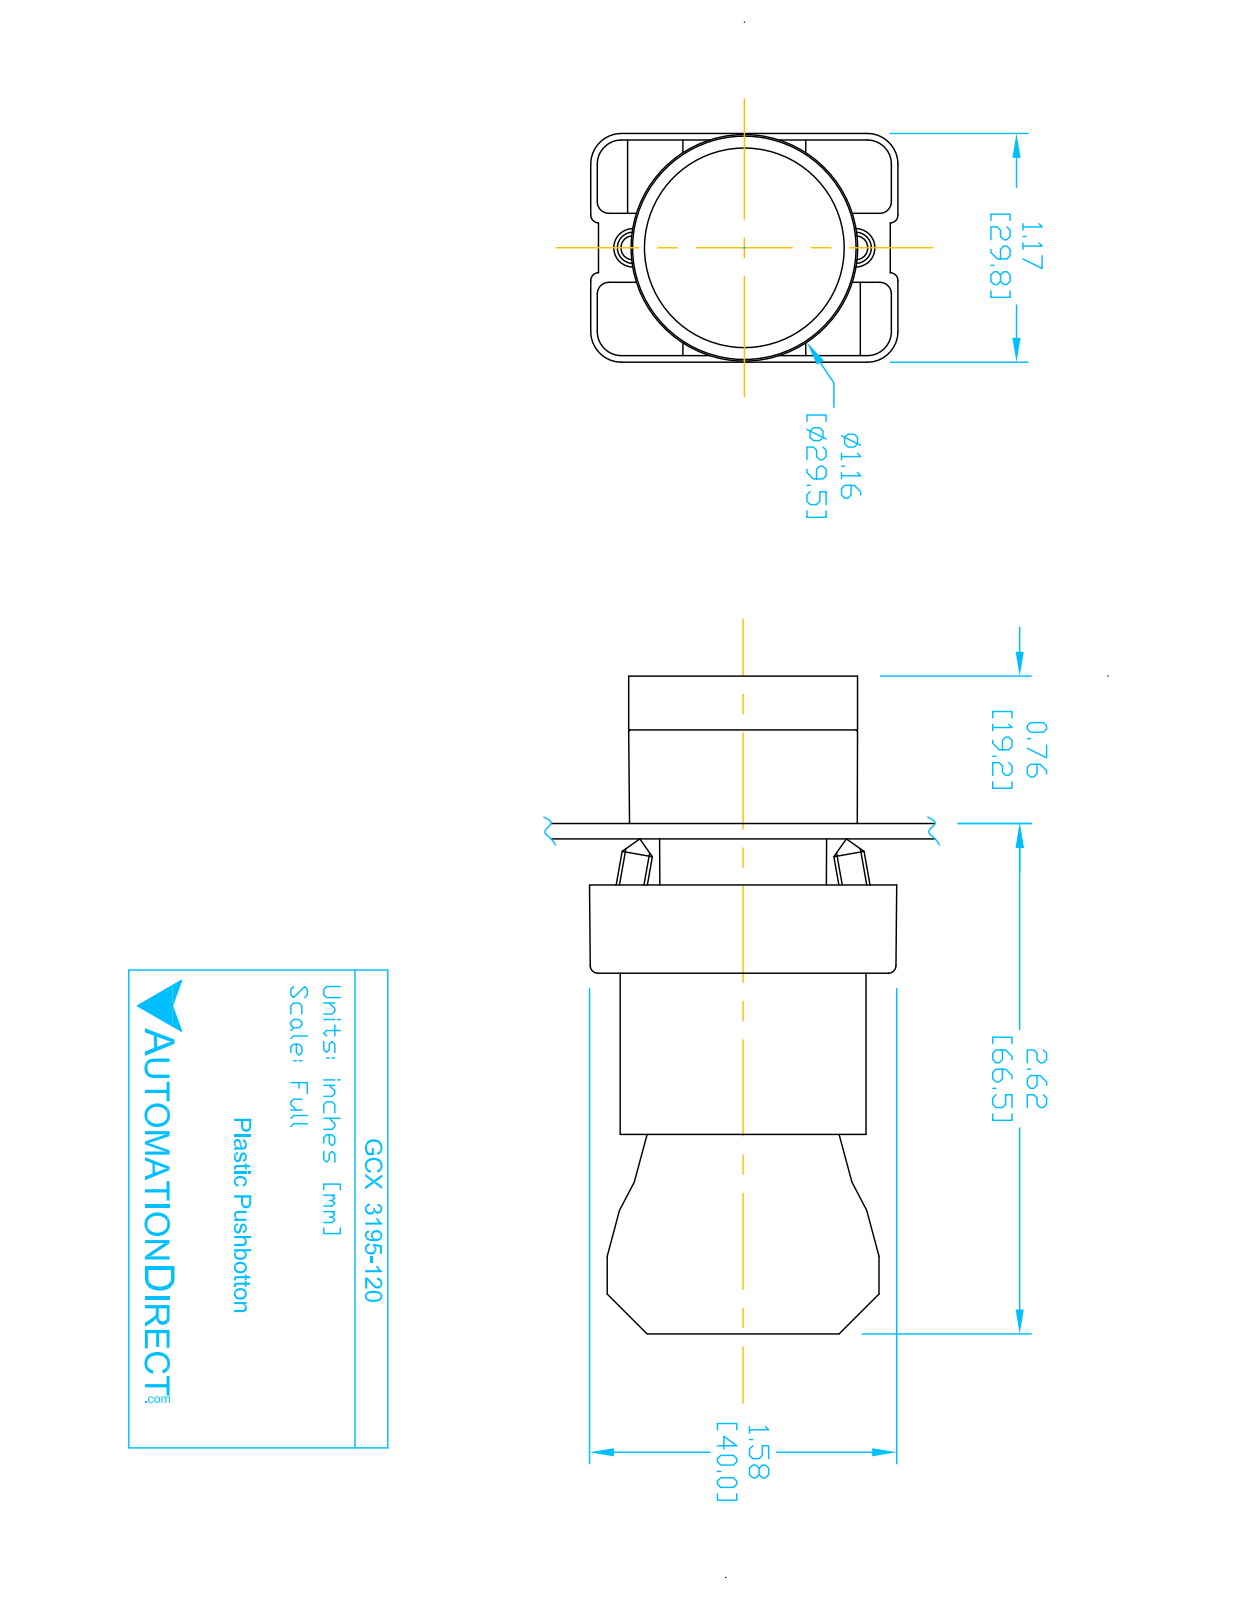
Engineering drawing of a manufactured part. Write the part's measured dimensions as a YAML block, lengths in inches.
part_name: "ECX3029-2; GCX3195 OPERATOR; GCX3195-120; ECX1050 (+1 more)"
step_written_by: "SolidWorks 2016 (AUTOMOTIVE_DESIGN)"
units: inches
bodies: {solids: 8, faces: 431, planar: 252, cylindrical: 148, other: 31}
overall_size: [3.319, 1.581, 1.177]
volume: 2.794
surface_area: 38.77
round_holes:
  - {diameter: 0.079, count: 2}
  - {diameter: 0.124, count: 2}
  - {diameter: 0.13, count: 2}
  - {diameter: 0.087, count: 1}
  - {diameter: 0.197, count: 1}
  - {diameter: 0.469, count: 1}
  - {diameter: 0.878, count: 1}
  - {diameter: 0.888, count: 1}
  - {diameter: 1.024, count: 1}
round_bosses_or_shafts:
  - {diameter: 0.157, count: 4}
  - {diameter: 1.175, count: 1}
  - {diameter: 1.004, count: 1}
  - {diameter: 0.945, count: 1}
  - {diameter: 0.856, count: 1}
  - {diameter: 0.78, count: 1}
  - {diameter: 0.504, count: 1}
partial_cylinders:
  - {radius: 0.059, count: 24}
  - {radius: 0.041, count: 12}
  - {radius: 0.124, count: 12}
  - {radius: 0.157, count: 12}
  - {radius: 0.039, count: 8}
  - {radius: 0.128, count: 2}
  - {radius: 0.02, count: 1}
  - {radius: 0.063, count: 1}
face_to_face_distances: [0.827, 0.579, 2.02, 1.193, 1.171, 0.276, 2.295, 1.469, 0.031, 0.033]
hole_center_spacings: [0.236, 0.544, 0.472, 0.49]
